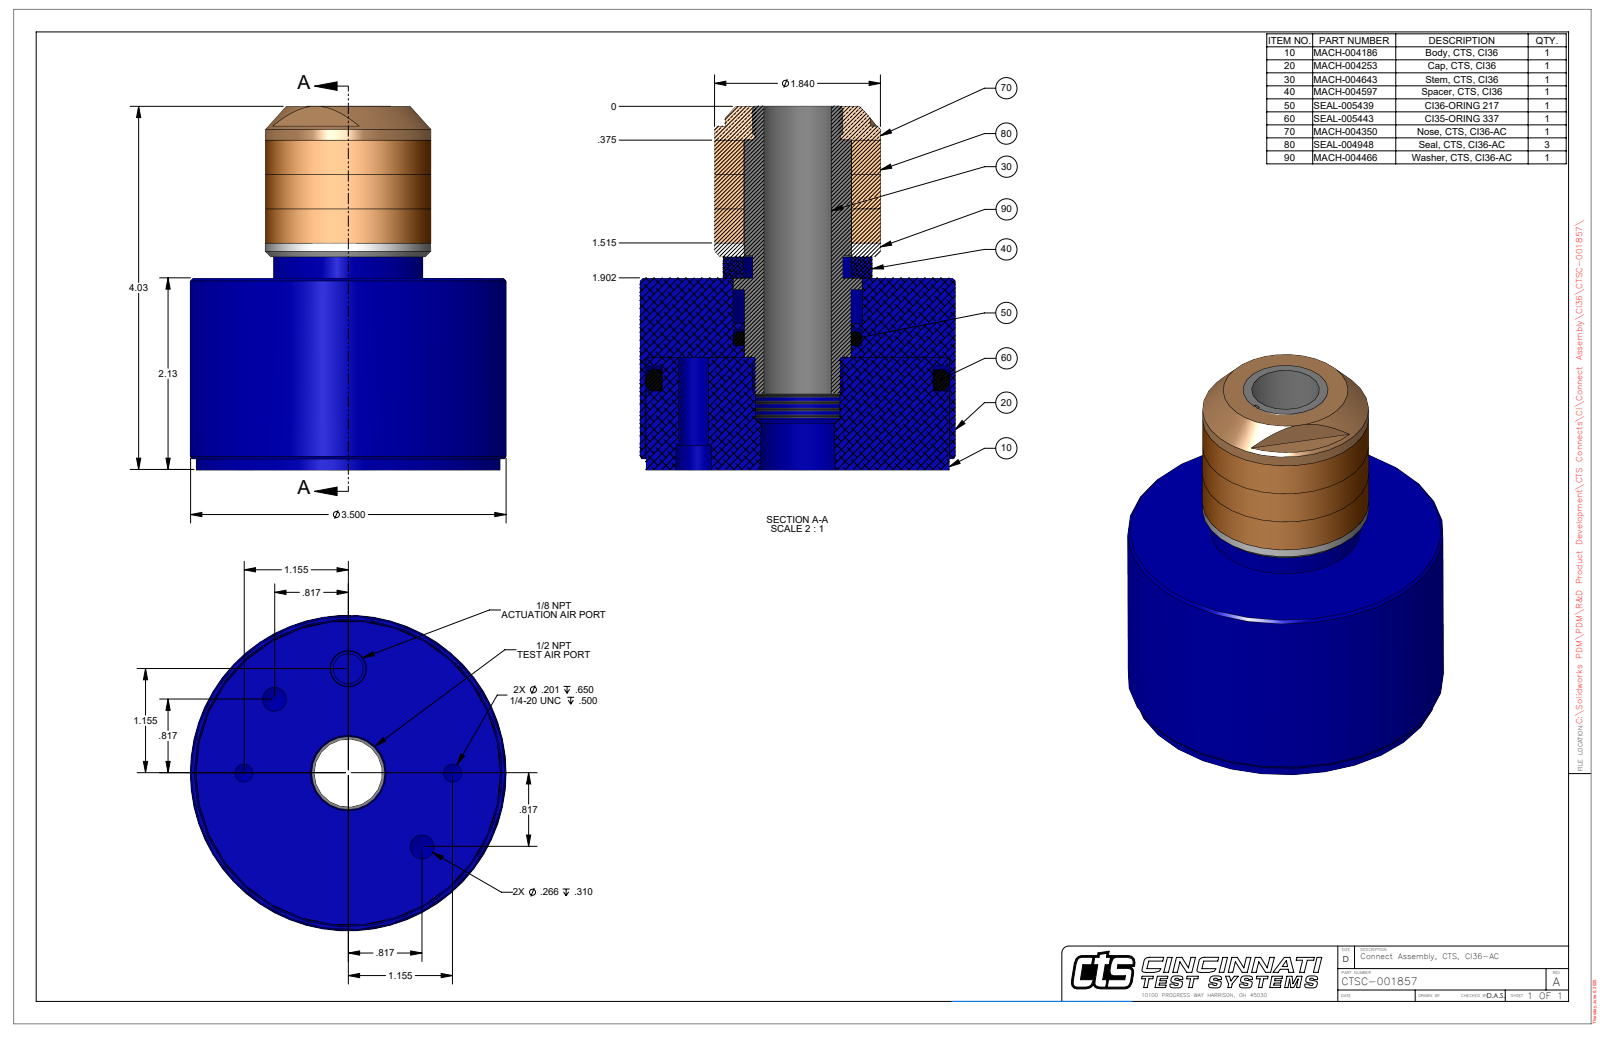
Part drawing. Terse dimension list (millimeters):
name: CTSC-001857
written by: SolidWorks 2023 (AUTOMOTIVE_DESIGN)
unit: mm
bodies: 1 solid, 79 faces (22 planar, 31 cylindrical, 26 other)
size: 102.4 × 88.9 × 88.9
volume: 376 700 mm³; area: 51 730 mm²
holes: 2× ⌀5.1, 2× ⌀6.8, 1× ⌀8.4, 1× ⌀19.1, 1× ⌀23.8, 1× ⌀36.5, 1× ⌀85.7
bosses: 1× ⌀88.9, 1× ⌀85.5, 1× ⌀46.7, 1× ⌀42.1, 1× ⌀36.2
rounds: 1× R11.7, 1× R17.5
face distances: 54, 102.3, 48.3, 21.4, 32.5, 80.8, 3.2, 18.3, 50.8, 99.1
hole spacings: 22.5, 29.3, 54.2, 29.3, 41.5, 58.6, 58.7
